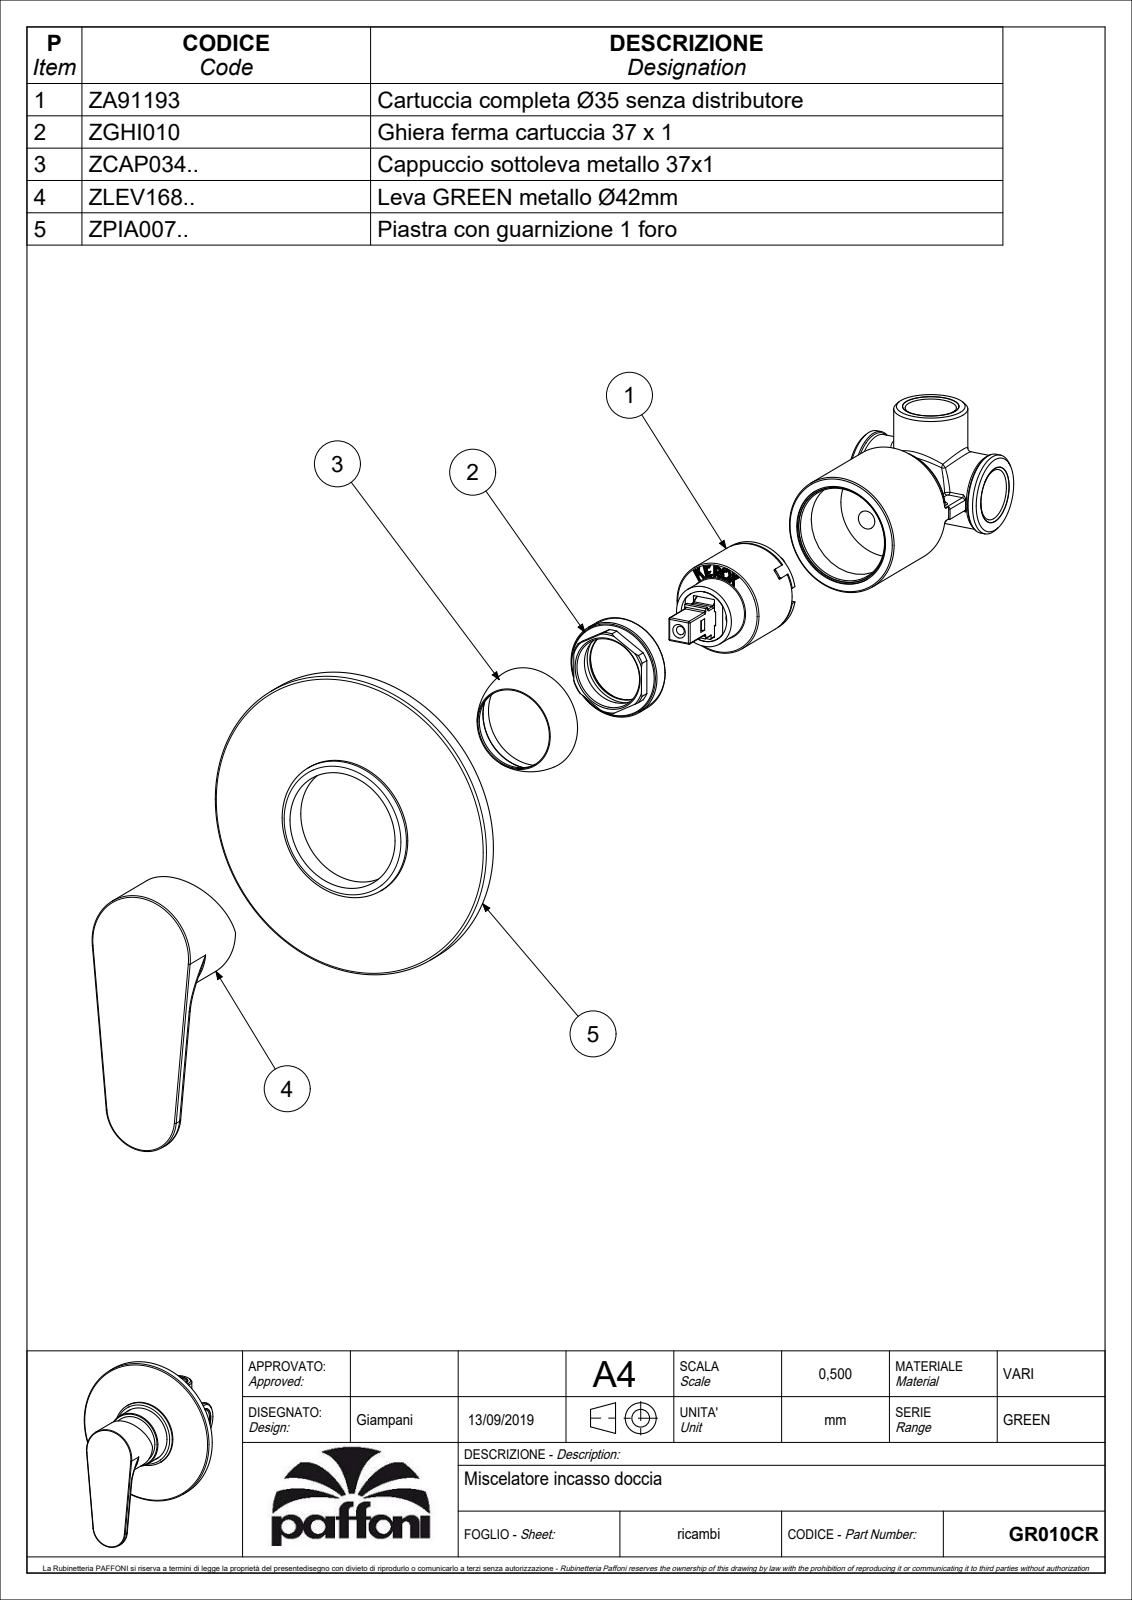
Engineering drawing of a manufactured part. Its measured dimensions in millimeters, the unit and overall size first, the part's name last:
Units: millimetres
Overall size (bounding box): 137.5 × 116 × 66.3
Round holes (diameter × count): ⌀3 ×1, ⌀4.2 ×1, ⌀5.5 ×1, ⌀39 ×1, ⌀45 ×1, ⌀50 ×1, ⌀114 ×1
Round bosses / shafts (diameter × count): ⌀116 ×1, ⌀53 ×1, ⌀44.8 ×1, ⌀42 ×1
Partial cylindrical surfaces — rounded edges, fillets, slot ends (radius × count): R0.5 ×2, R3 ×2, R3.8 ×1, R15 ×1
Main face-to-face distances: 66.3, 66.26, 60.3, 2.5, 3.5, 6, 60.26, 63.8, 63.76, 20.8
Volume: 90 186 mm³ · Surface area: 67 287 mm²
Bodies: 2 solids, 116 faces (46 planar, 39 cylindrical, 31 other)
Part name (STEP PRODUCT): GR010CR
STEP written by: CREO PARAMETRIC BY PTC INC, 2020044 (CONFIG_CONTROL_DESIGN)
